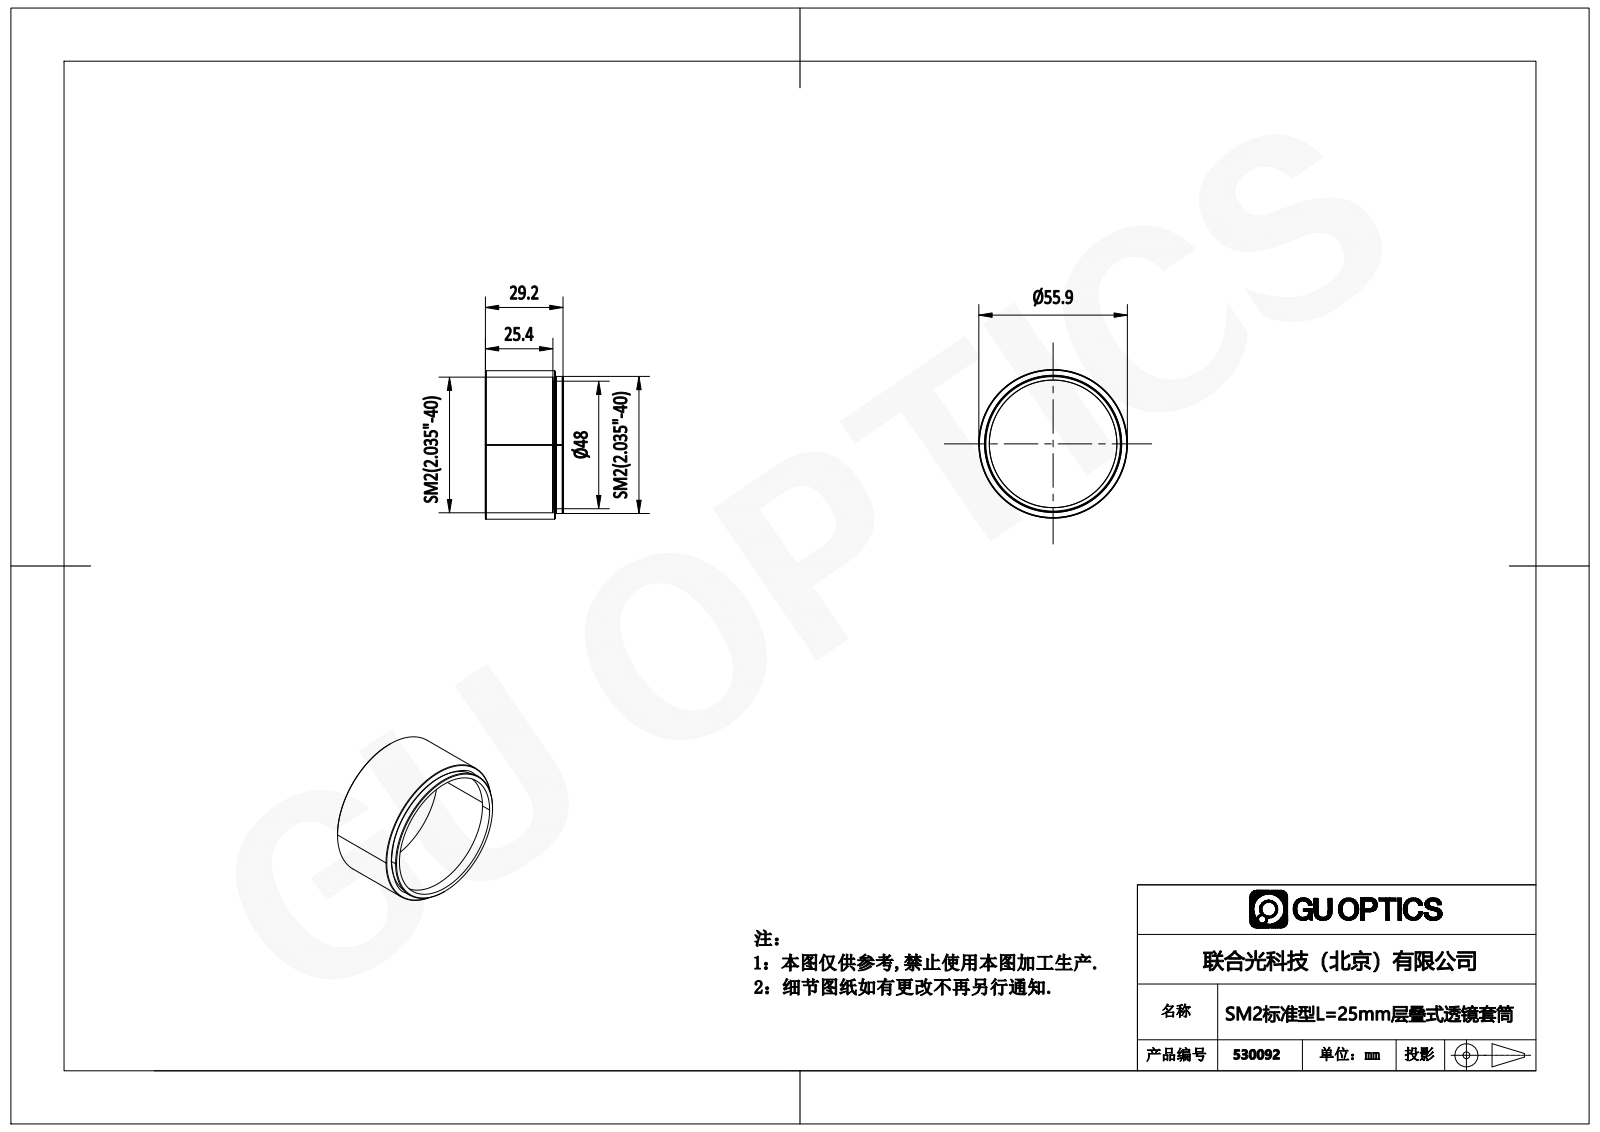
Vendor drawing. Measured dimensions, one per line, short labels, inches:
written by: SolidWorks 2018 (AUTOMOTIVE_DESIGN)
unit: in
bodies: 0 solids, 36 faces (13 planar, 12 cylindrical, 11 other)
size: 2.201 × 2.201 × 1.15
holes: 1× ⌀1.878, 1× ⌀1.89, 1× ⌀2.01
bosses: 1× ⌀2.201, 1× ⌀2.031, 1× ⌀1.992
face distances: 1.031, 0.118, 1.15, 1, 0.031, 0.15, 0.882, 0.913, 0.02, 0.098
